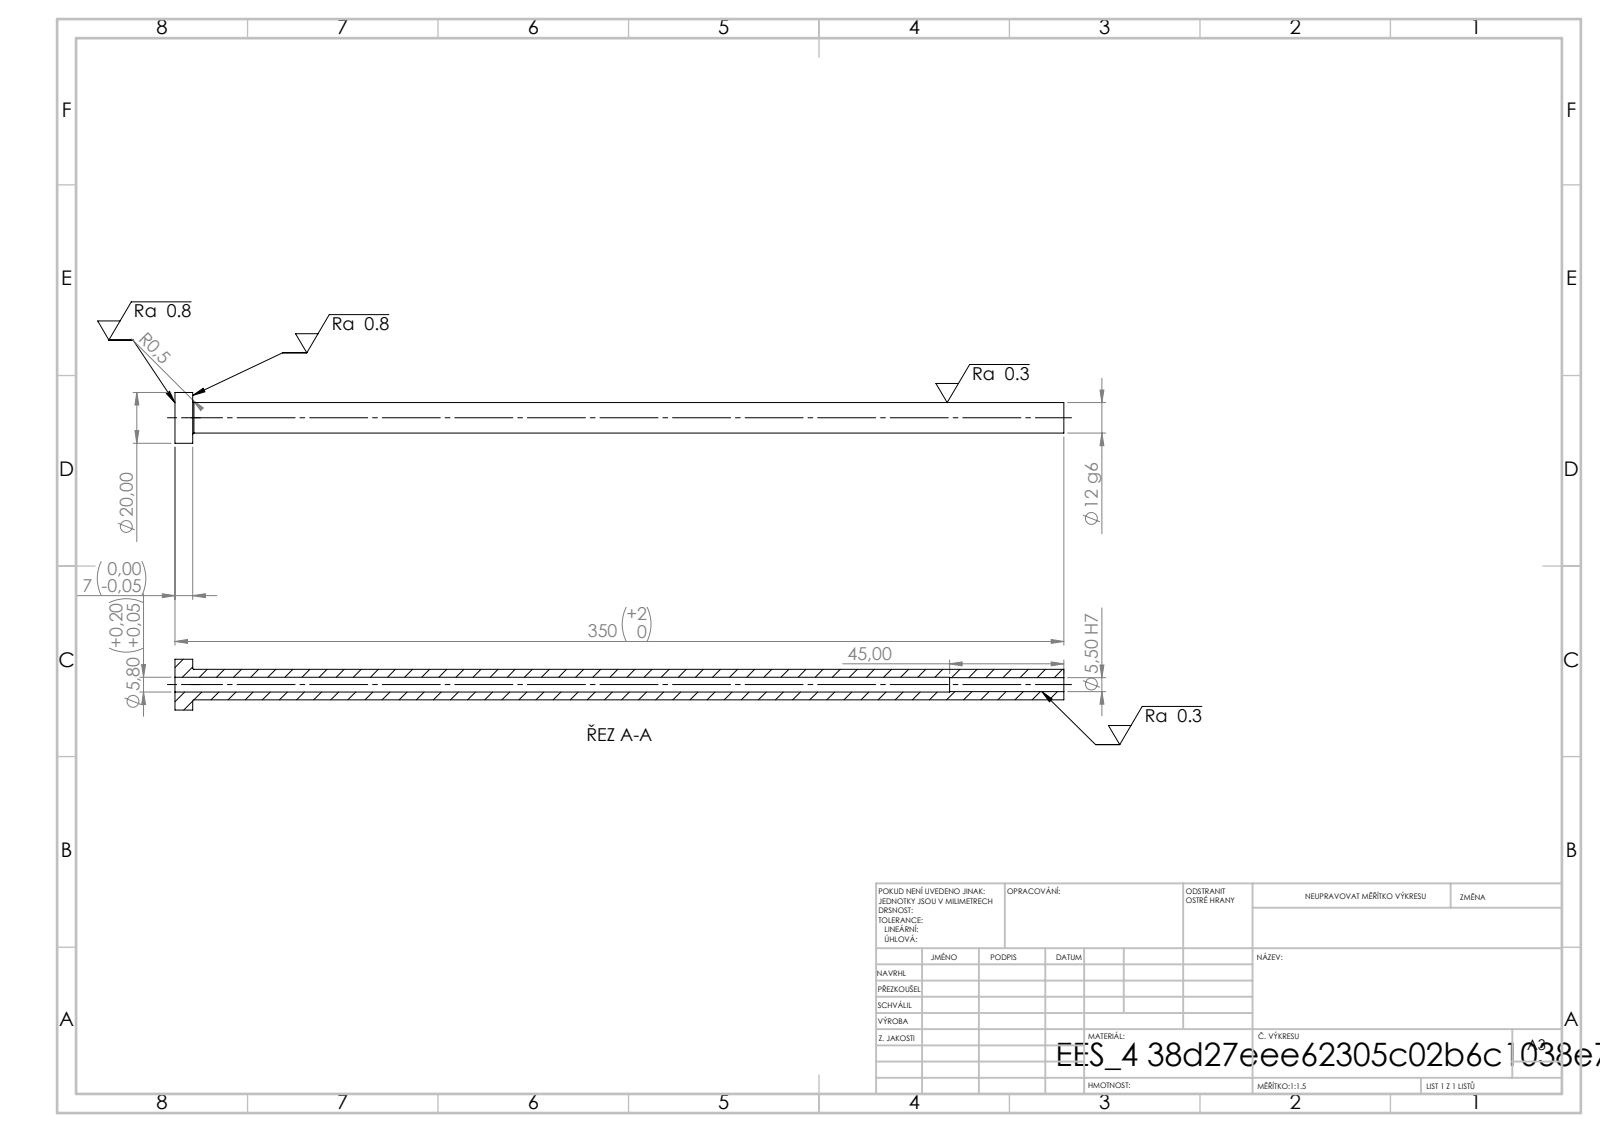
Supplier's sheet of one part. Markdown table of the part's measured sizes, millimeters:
| quantity | value |
| --- | --- |
| STEP written by | SolidWorks 2019 (CONFIG_CONTROL_DESIGN) |
| units | millimeters |
| bodies | 1 solid, 14 faces (4 planar, 8 cylindrical, 2 other) |
| overall size | 350 × 20 × 20 |
| volume | 31 866 mm³ |
| surface area | 20 278 mm² |
| round holes (diameter × count) | 5.5 × 1, 5.8 × 1 |
| round bosses / shafts (diameter × count) | 20 × 1, 12 × 1 |
| main face-to-face distances | 7, 350, 343, 305, 298, 45 |
